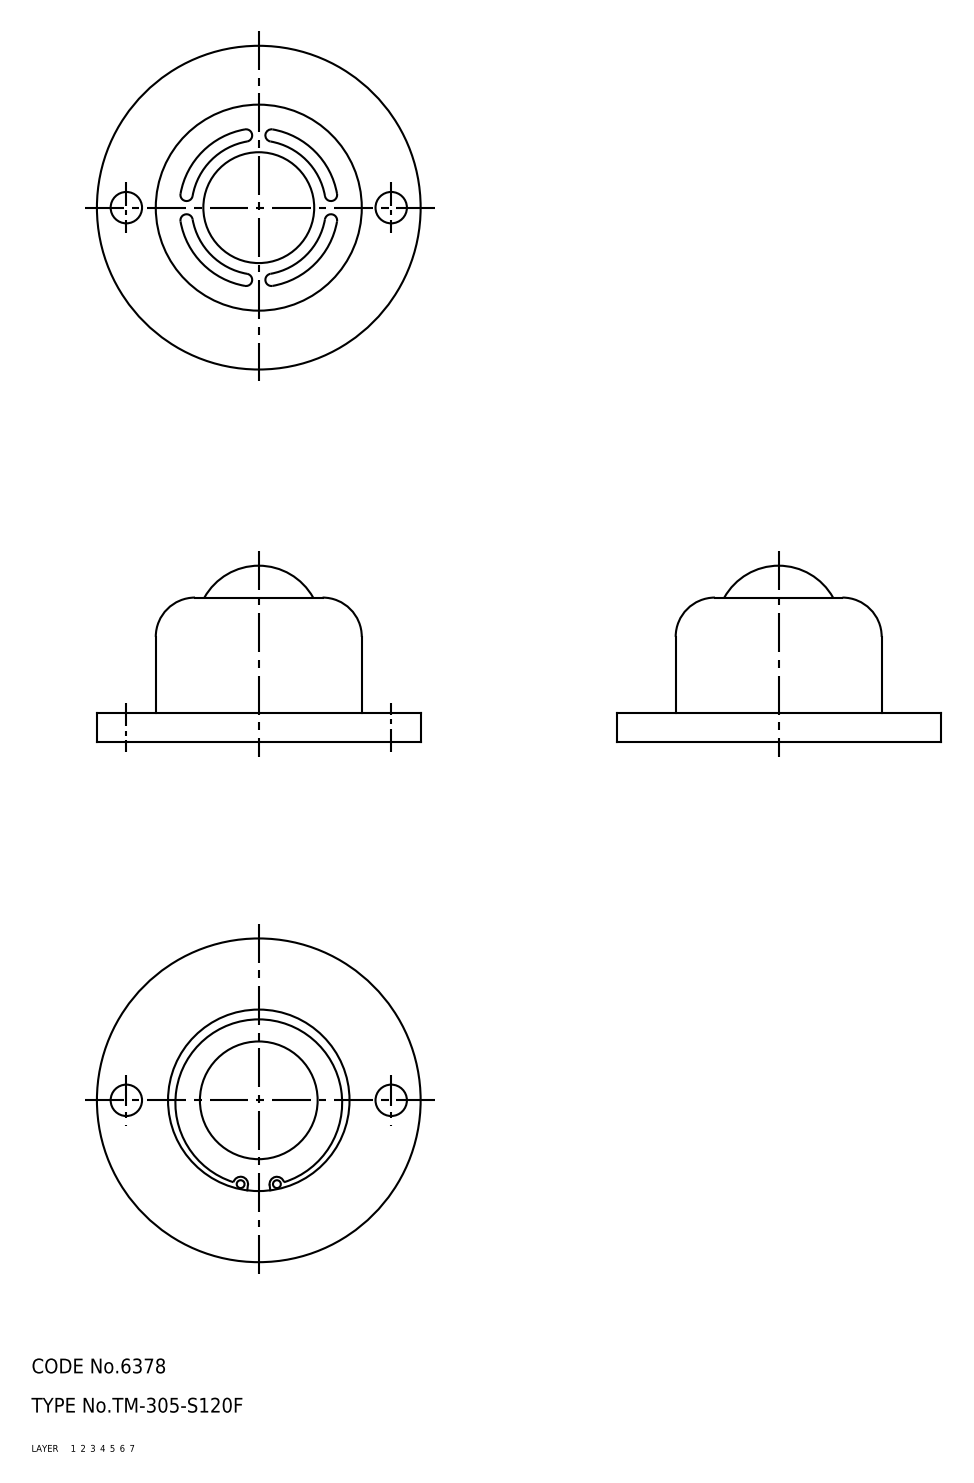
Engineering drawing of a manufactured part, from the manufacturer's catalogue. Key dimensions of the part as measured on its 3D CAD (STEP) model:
Part name (STEP PRODUCT): 67113745; 67113758
STEP written by: CADfix (AUTOMOTIVE_DESIGN)
Units: millimetres
Bodies: 2 solids, 57 faces (0 planar, 0 cylindrical, 57 other)
Overall size (bounding box): 66 × 66 × 36
Volume: 29 433 mm³ · Surface area: 17 449 mm²
